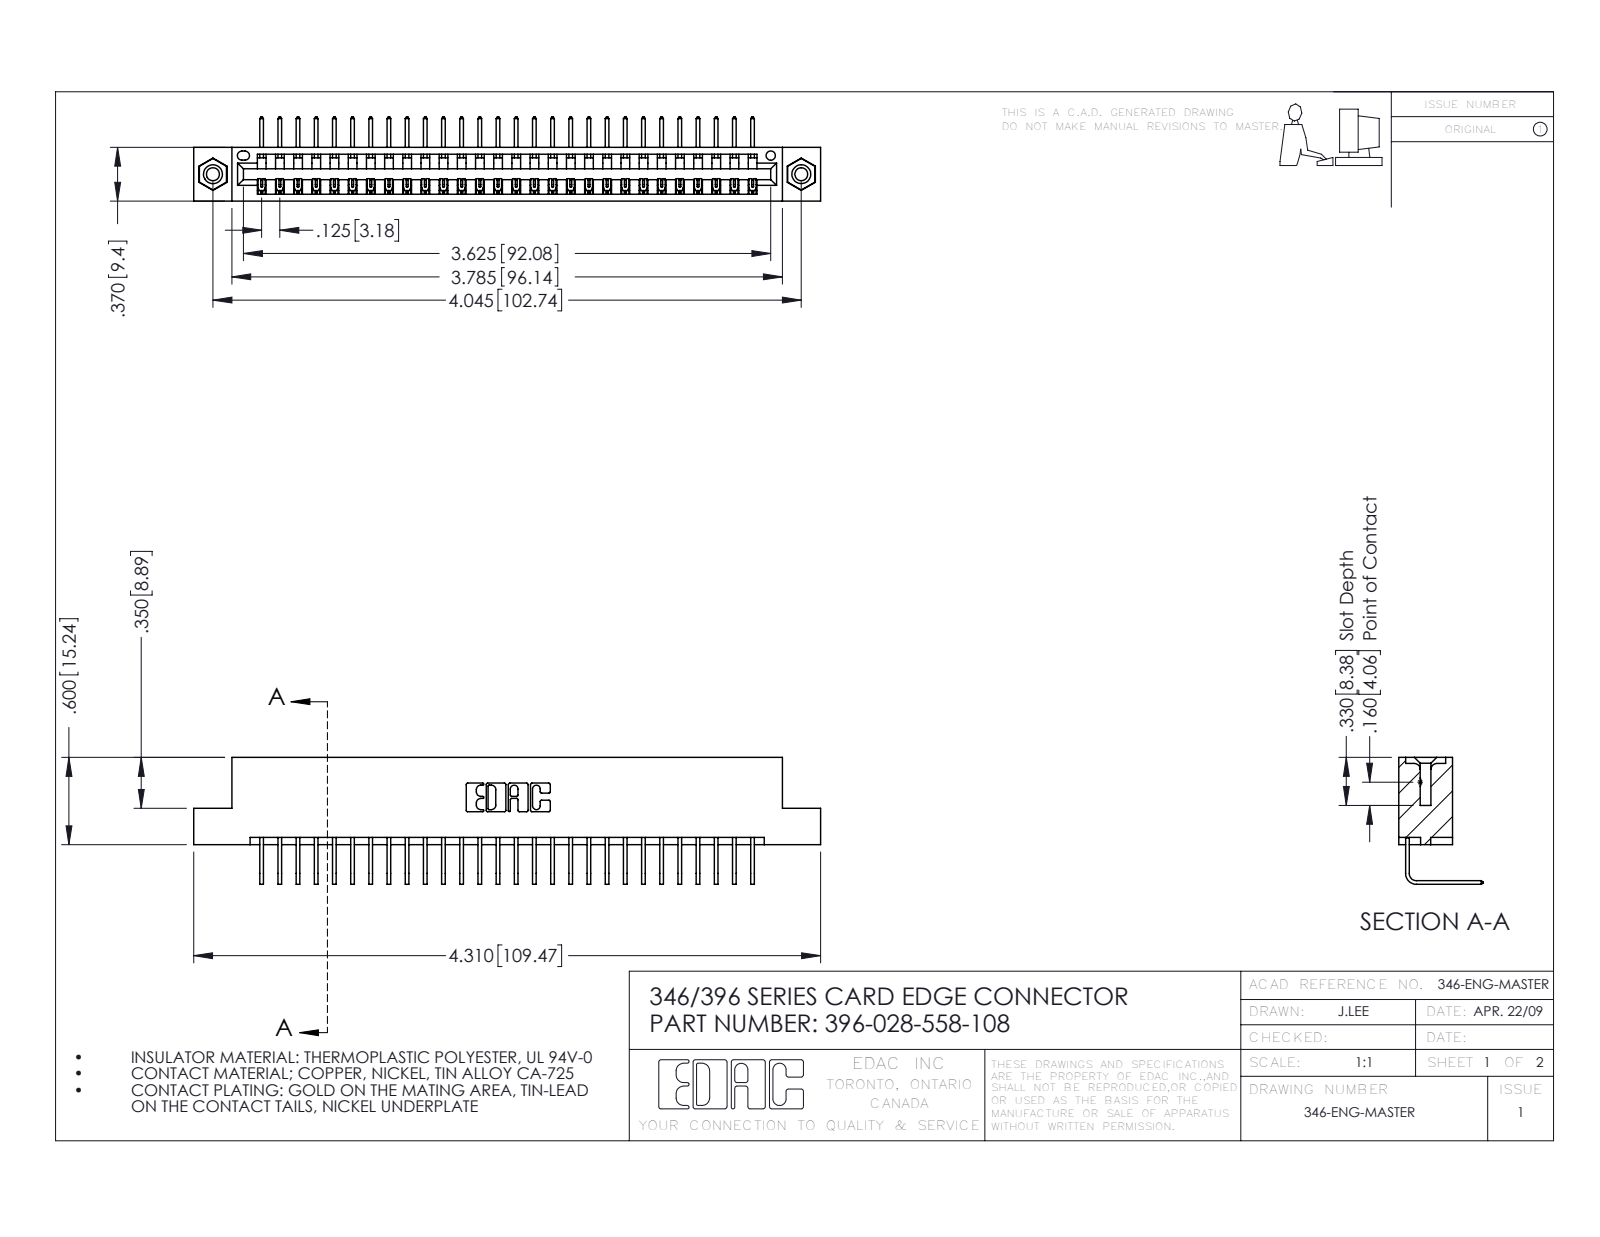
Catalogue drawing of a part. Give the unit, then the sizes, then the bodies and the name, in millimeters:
Units: millimetres
Overall size (bounding box): 109.5 × 22.2 × 14.7
Round holes (diameter × count): ⌀2.3 ×2, ⌀3.2 ×2, ⌀4 ×2, ⌀1.6 ×1
Round bosses / shafts (diameter × count): ⌀3.9 ×2
Partial cylindrical surfaces — rounded edges, fillets, slot ends (radius × count): R0.2 ×56, R0.3 ×22, R0.2 ×6, R0.8 ×6, R0.7 ×3, R0.8 ×2, R1 ×2, R0.4 ×1
Main face-to-face distances: 8.2, 1.2, 9.4, 6.4, 7.6, 0.6, 1.8, 3.8, 5.6, 2.5
Hole centre spacings: 6.2, 97.5, 102.7
Volume: 10 500 mm³ · Surface area: 13 510 mm²
Bodies: 31 solids, 1862 faces (1284 planar, 562 cylindrical, 16 other)
Part name (STEP PRODUCT): 396-028-558-108; 346 Part_Flush Mounting Lugs - 0.156 Dia-TI; 345-292-001_558 Tail - 2; 345-250-001_345-250-003-102
STEP written by: SolidWorks 2016 (CONFIG_CONTROL_DESIGN)
